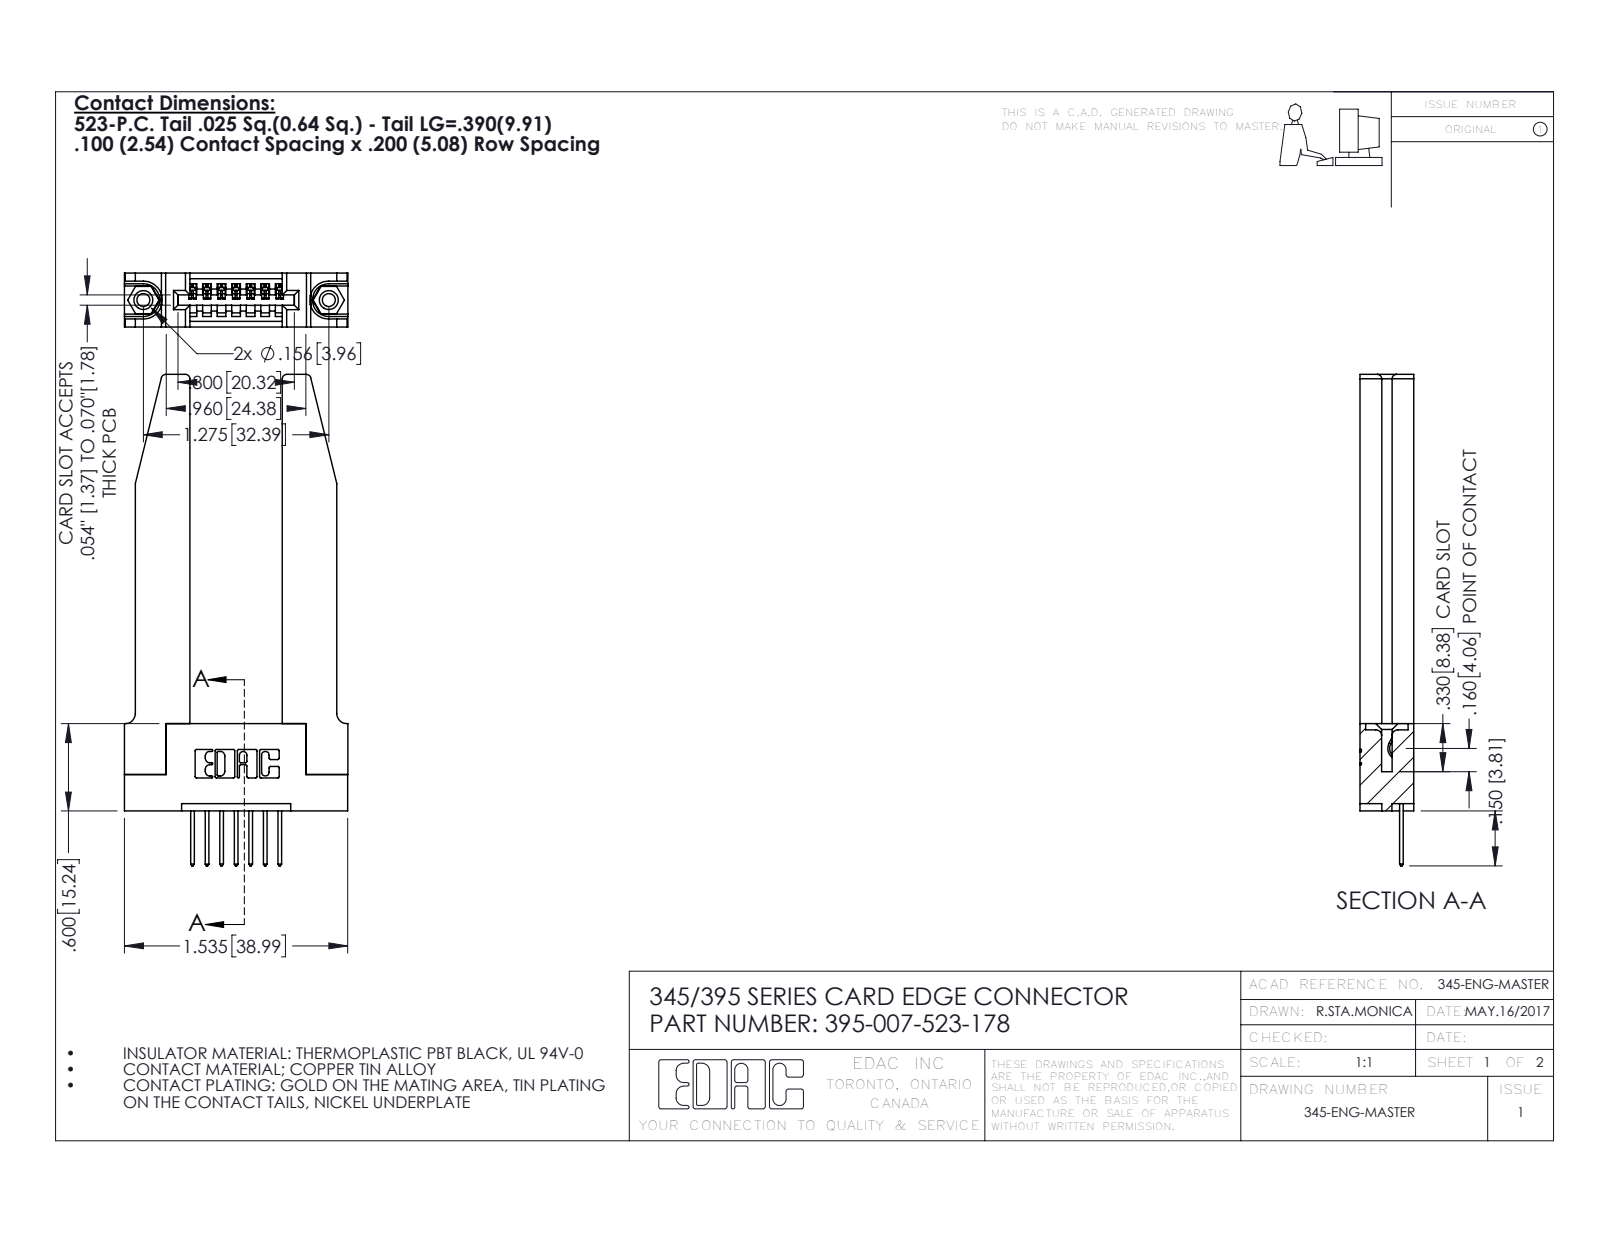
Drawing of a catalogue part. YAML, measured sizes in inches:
part_name: "345-292-001_345-293-123; 345 Part_Flush Mounting Lugs - 0.156 Dia-TH; 395-007-523-178; 345-220-078_345-220-078 (+1 more)"
step_written_by: "SolidWorks 2016 (CONFIG_CONTROL_DESIGN)"
units: inches
bodies: {solids: 12, faces: 766, planar: 502, cylindrical: 212, other: 52}
overall_size: [3.377, 1.536, 0.37]
volume: 0.683
surface_area: 16.92
round_holes:
  - {diameter: 0.089, count: 2}
  - {diameter: 0.125, count: 2}
  - {diameter: 0.156, count: 2}
  - {diameter: 0.064, count: 1}
round_bosses_or_shafts:
  - {diameter: 0.155, count: 2}
partial_cylinders:
  - {radius: 0.01, count: 22}
  - {radius: 0.006, count: 14}
  - {radius: 0.01, count: 14}
  - {radius: 0.03, count: 8}
  - {radius: 0.007, count: 6}
  - {radius: 0.031, count: 6}
  - {radius: 0.026, count: 3}
  - {radius: 0.031, count: 2}
face_to_face_distances: [0.37, 0.15, 0.22, 0.072, 0.148, 0.298, 0.635, 0.077, 0.2, 0.095]
hole_center_spacings: [0.27, 1.045, 1.275]
